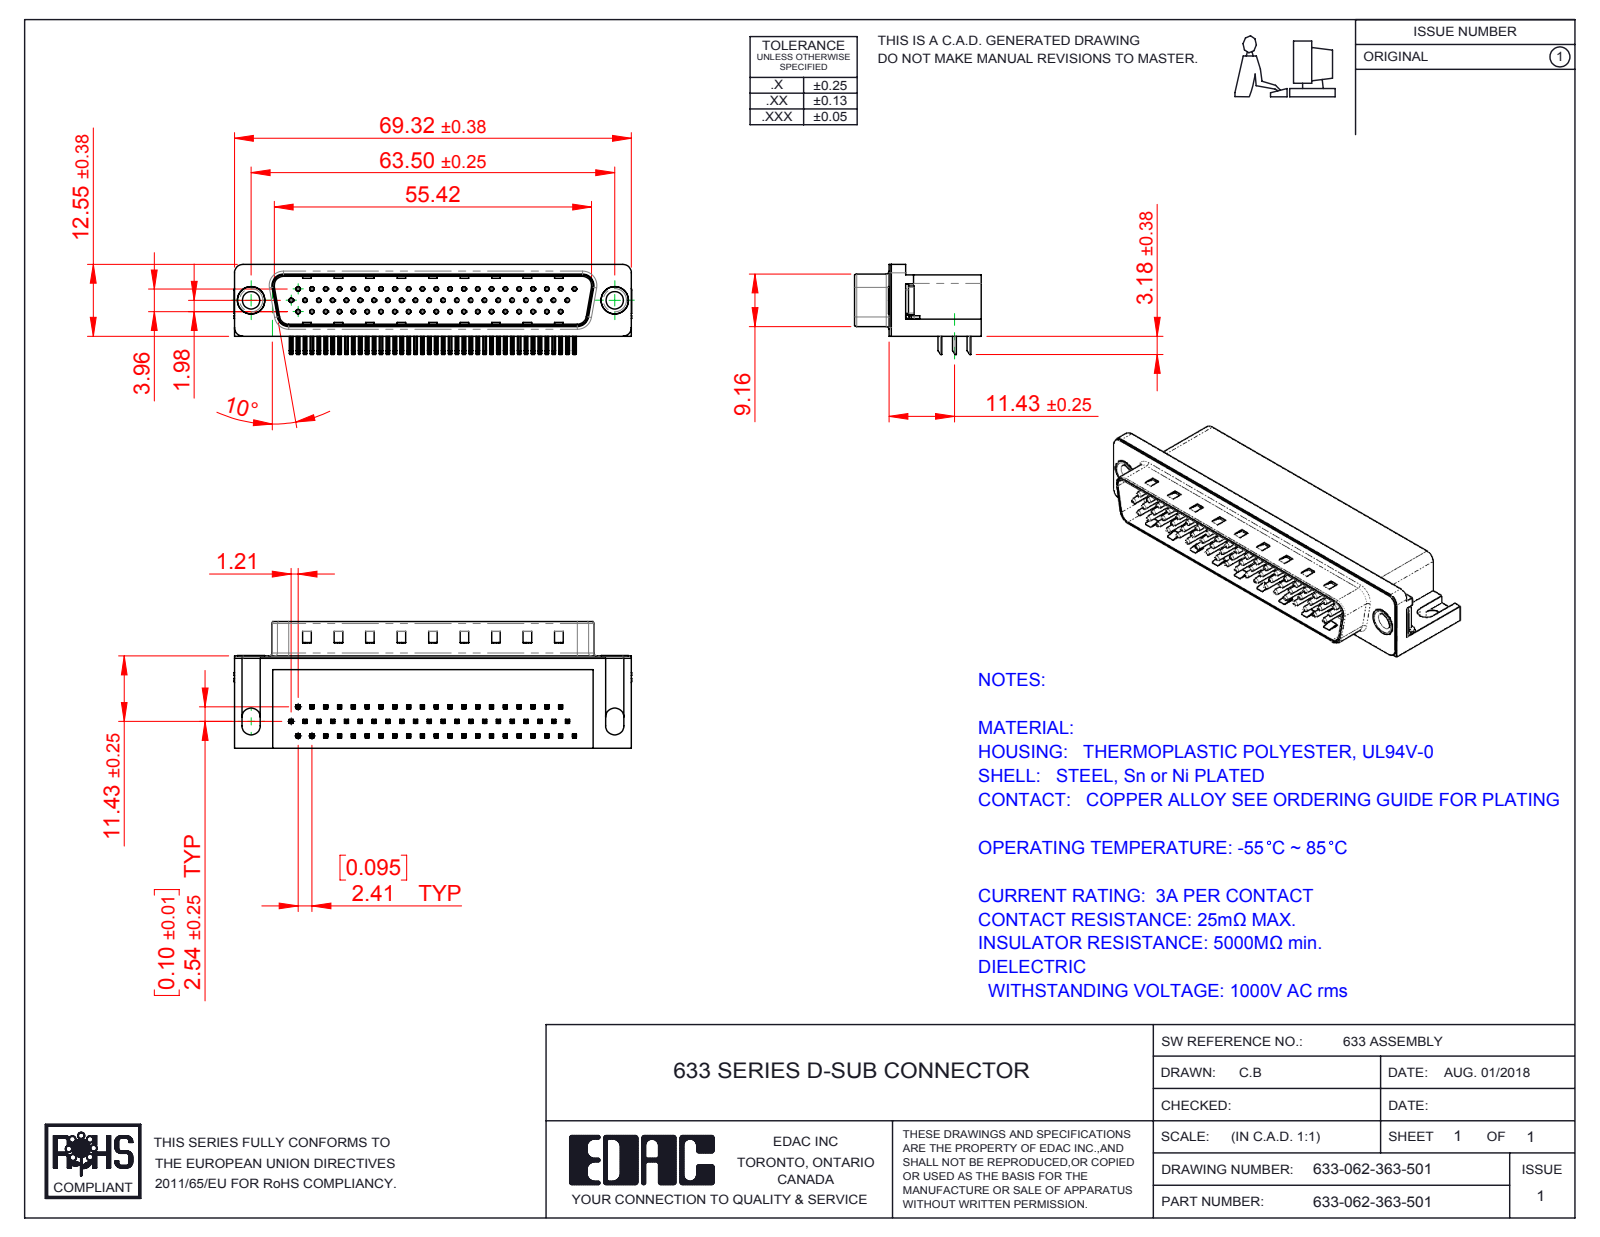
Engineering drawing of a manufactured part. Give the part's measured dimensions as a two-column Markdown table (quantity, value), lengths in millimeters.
| quantity | value |
| --- | --- |
| part name | 633 Contact Top; 633 Non Board Mount; 633 Housing_62 Contact; 633 Thru Hole Rivet (+4 more) |
| STEP written by | SolidWorks 2016 (CONFIG_CONTROL_DESIGN) |
| units | millimeters |
| bodies | 68 solids, 5032 faces (3213 planar, 1420 cylindrical, 399 other) |
| overall size | 69.4 × 22.1 × 15.73 |
| volume | 10 996 mm³ |
| surface area | 13 163 mm² |
| round holes (diameter × count) | 0.35 × 62, 0.8 × 62, 3.05 × 2, 4 × 2, 4.8 × 2, 5 × 2 |
| round bosses / shafts (diameter × count) | 0.75 × 62, 4.9 × 2, 4.75 × 2, 3.85 × 2 |
| partial cylindrical surfaces (radius × count) | 0.25 × 256, 0.12 × 124, 1 × 16, 0.5 × 9, 1.6 × 8, 1.5 × 7, 0.9 × 4, 2 × 4 |
| main face-to-face distances | 0.4, 10.35, 15.7, 8.76, 2.5, 2.54, 2.9, 8.36, 2.1, 8.6 |
| hole center spacings | 2.41, 4.82, 7.24, 9.65, 14.48, 16.89, 4.83, 7.23 |
